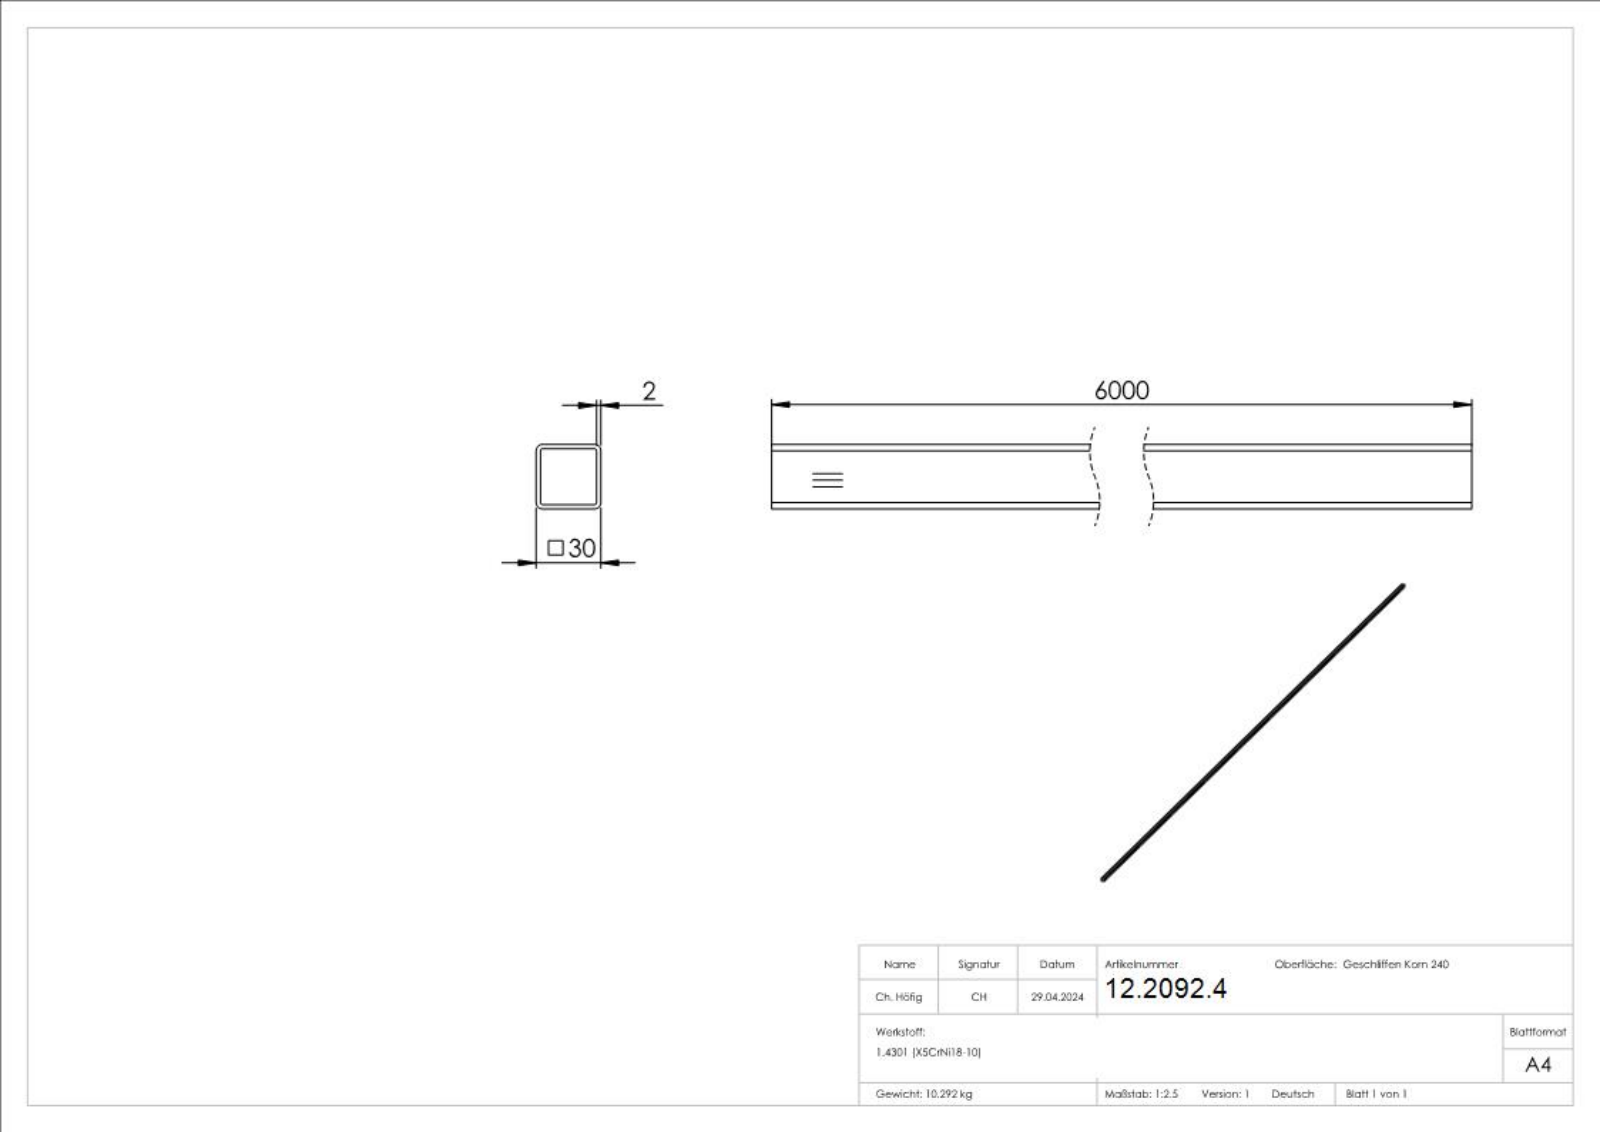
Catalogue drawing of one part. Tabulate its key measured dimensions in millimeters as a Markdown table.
| quantity | value |
| --- | --- |
| part name | 55399-240 |
| STEP written by | SolidWorks 2018 (CONFIG_CONTROL_DESIGN) |
| units | millimeters |
| bodies | 1 solid, 294 faces (155 planar, 8 cylindrical, 131 other) |
| overall size | 6000 × 30 × 30 |
| volume | 1 303 000 mm³ |
| surface area | 1 303 000 mm² |
| partial cylindrical surfaces (radius × count) | 1 × 4, 3 × 4 |
| main face-to-face distances | 2, 28, 30, 26, 6000, 1.9, 26.1, 28.1, 0.88, 1.82 |
